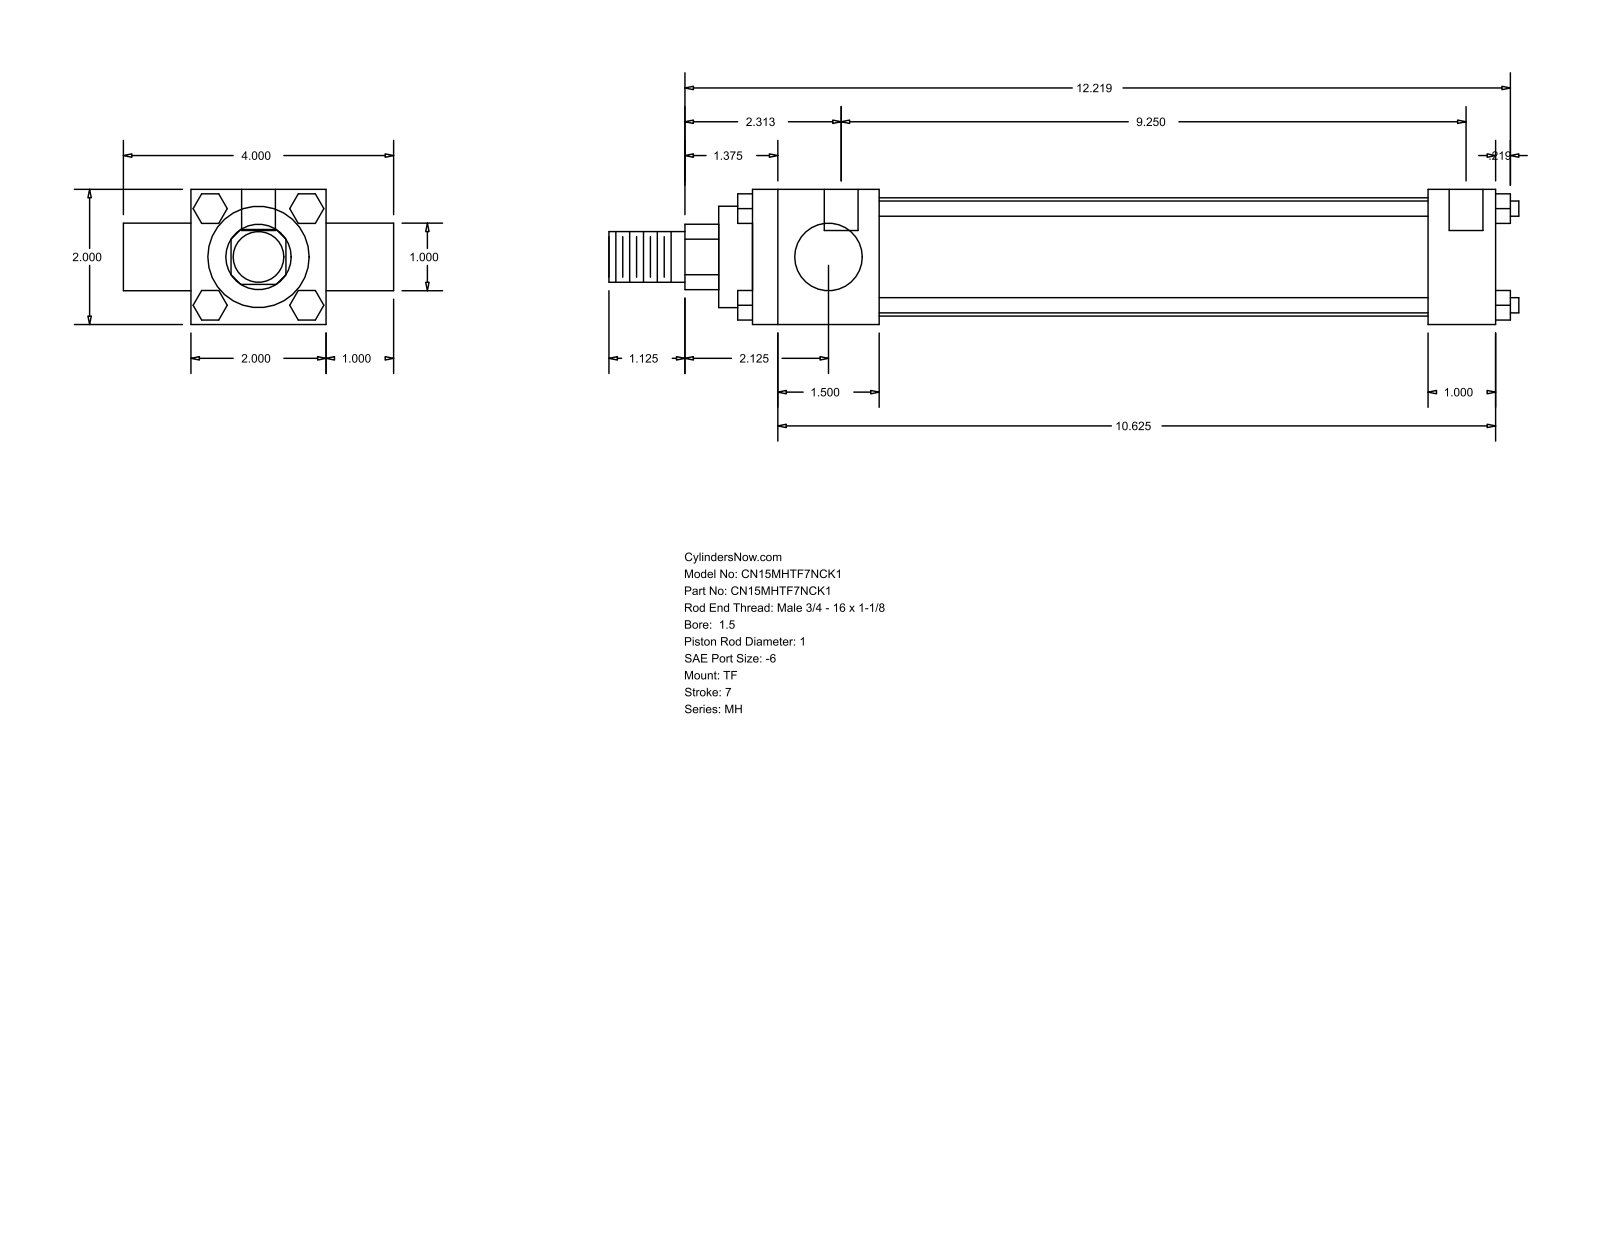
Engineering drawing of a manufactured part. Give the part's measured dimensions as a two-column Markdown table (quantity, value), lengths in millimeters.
| quantity | value |
| --- | --- |
| part name | MH_TF__0150_1 |
| STEP written by | GSSL Pune (CONFIG_CONTROL_DESIGN) |
| units | millimeters |
| bodies | 0 solids, 120 faces (92 planar, 28 cylindrical, 0 other) |
| overall size | 342.11 × 101.6 × 50.8 |
| round holes (diameter × count) | 5.56 × 3, 12.7 × 2 |
| round bosses / shafts (diameter × count) | 5.71 × 4, 25.4 × 2, 44.45 × 1, 38.1 × 1, 19.05 × 1 |
| partial cylindrical surfaces (radius × count) | 12.29 × 1 |
| main face-to-face distances | 50.8, 25.4, 279.4, 76.2, 47.63, 231.77, 254, 206.37, 101.6, 12.7 |
| hole center spacings | 3.18, 234.95, 238.13 |
